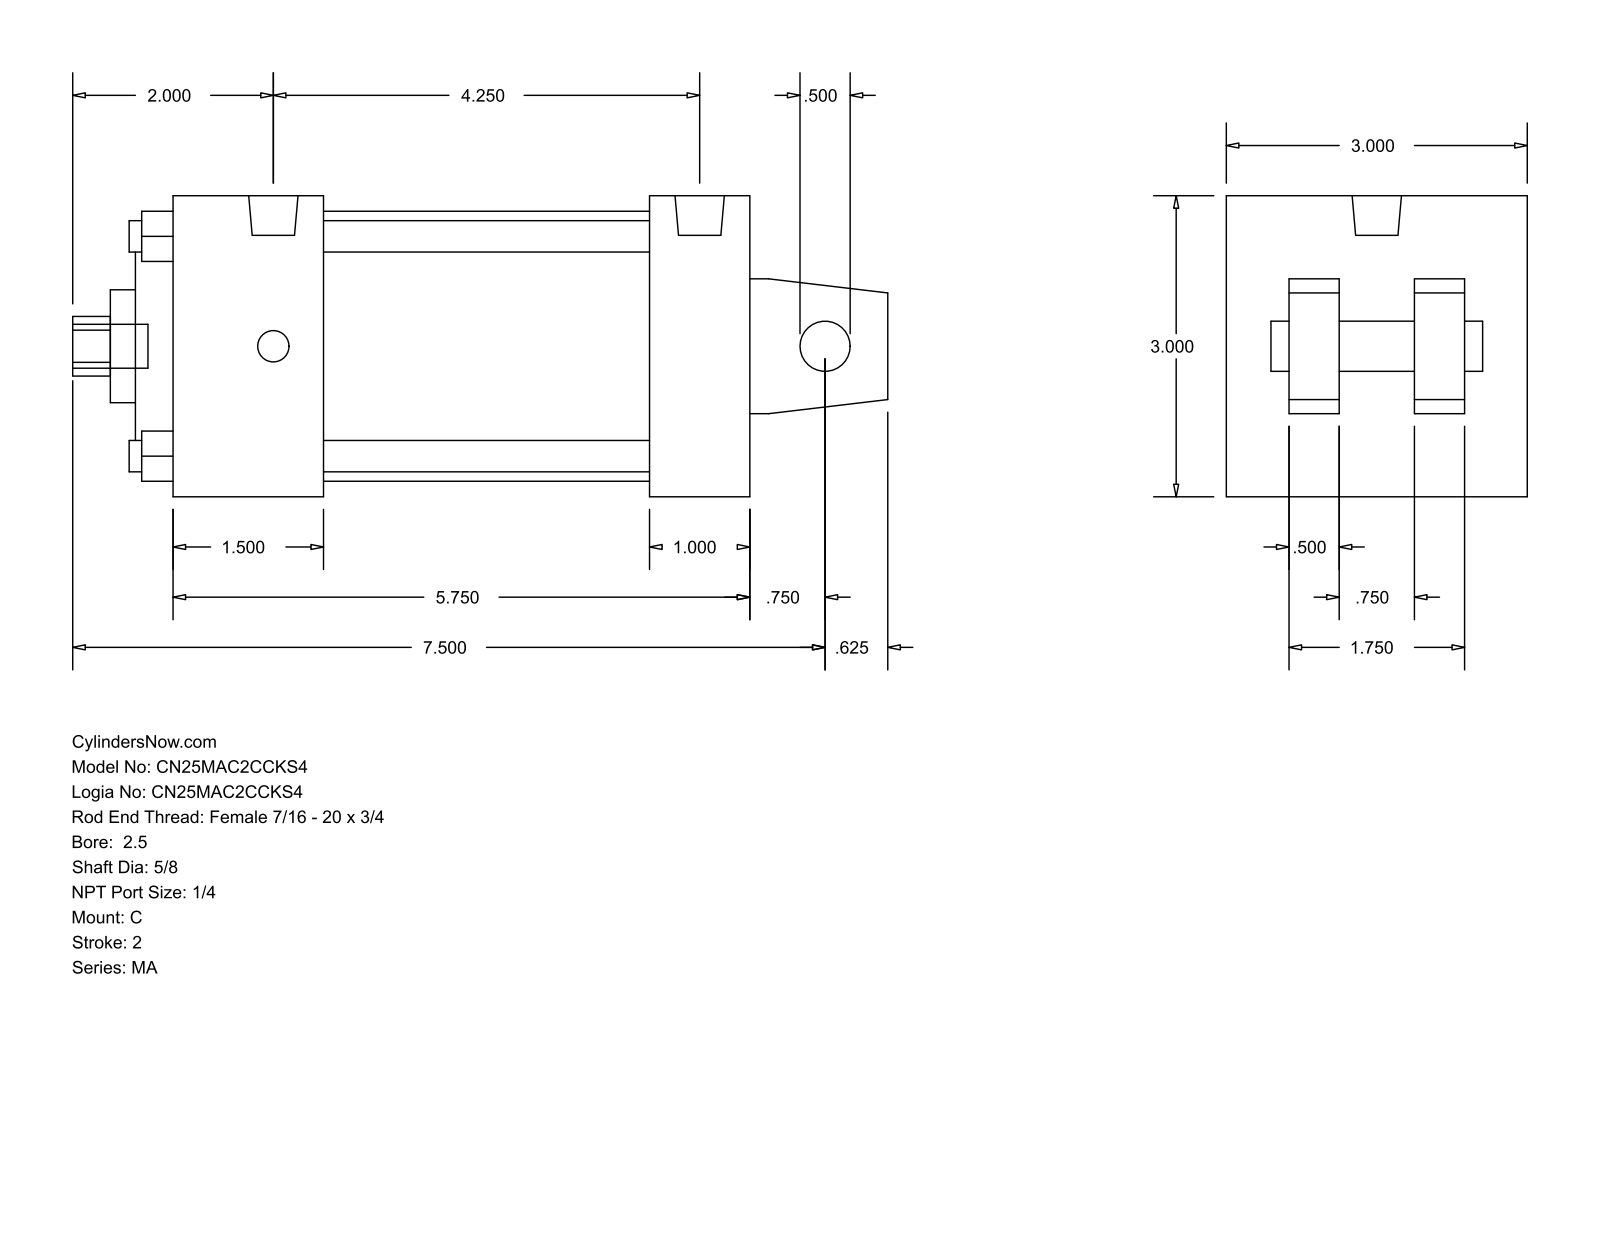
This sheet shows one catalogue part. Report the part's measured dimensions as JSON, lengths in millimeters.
{"part_name": "MA_C__0250_0.625", "step_written_by": "GSSL Pune (CONFIG_CONTROL_DESIGN)", "units": "millimeters", "bodies": {"solids": 0, "faces": 105, "planar": 77, "cylindrical": 28, "other": 0}, "overall_size": [206.38, 76.2, 76.2], "round_holes": [[7.94, 4], [12.7, 1], [15.88, 1], [28.57, 1], [50.8, 1], [68.33, 1]], "round_bosses_or_shafts": [[7.94, 4], [12.49, 2], [11.11, 1]], "partial_cylinders_radius": [[7.54, 1]], "face_to_face_distances": [76.2, 146.05, 12.7, 15.87, 60.33, 47.63, 25.4, 38.1, 120.65, 82.55], "hole_center_spacings": [39.33, 55.62, 78.66]}
